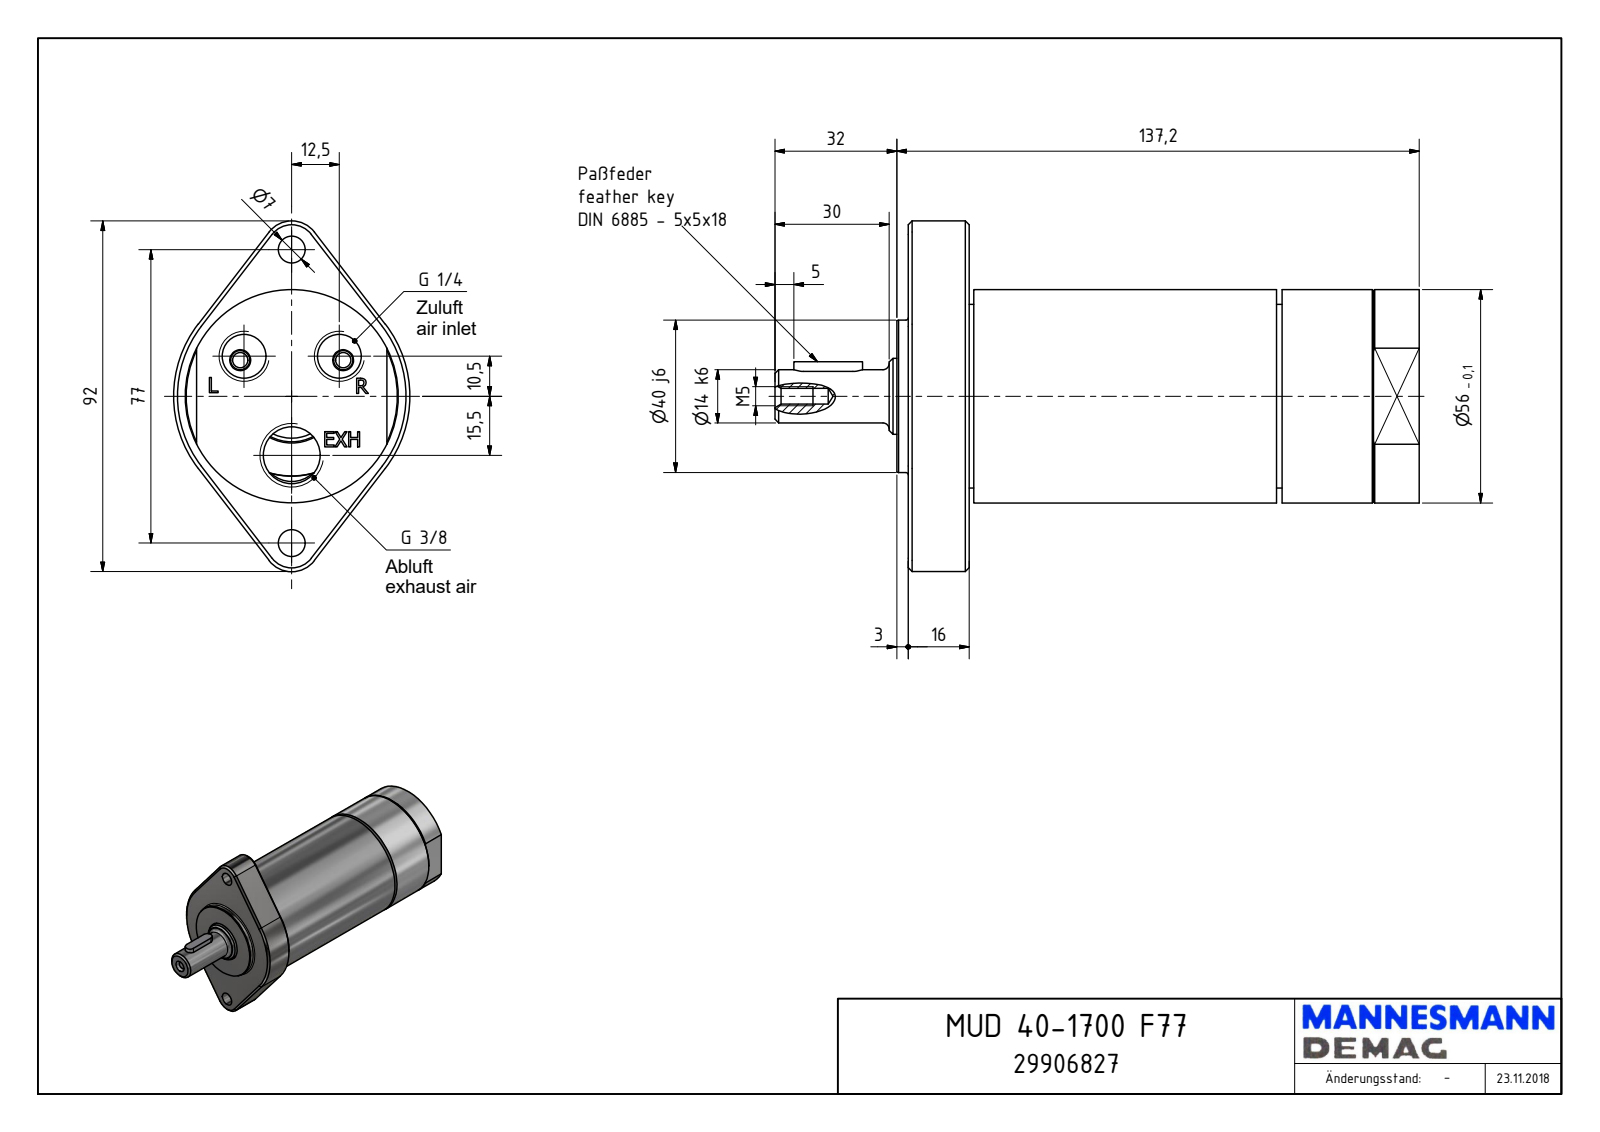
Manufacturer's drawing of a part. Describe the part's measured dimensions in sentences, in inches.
The part is named "MUD 40-1700 F77_29906827". Its 3-D file was written by "Autodesk Inventor 2018 (AUTOMOTIVE_DESIGN)". It is 1 solid with 189 faces: 104 planar, 35 cylindrical and 50 other. Overall it measures 6.661 by 3.622 by 2.441 inches. Its volume is 21.41 cubic inches and its surface area 62.99 square inches. Round holes: 2 of diameter 0.276, 2 of diameter 0.451, 1 of diameter 0.163, 1 of diameter 0.589, 1 of diameter 0.827, 1 of diameter 0.837, 1 of diameter 0.927, 1 of diameter 1.024, 1 of diameter 1.905. Round bosses or shafts: 1 of diameter 2.205, 1 of diameter 1.897, 1 of diameter 1.575, 1 of diameter 0.785, 1 of diameter 0.551. Partial cylindrical surfaces (rounded edges, fillets, slot ends): 2 of radius 0.098, 2 of radius 0.236, 2 of radius 0.295, 1 of radius 0.851, 1 of radius 0.906, 1 of radius 1.22. The main face-to-face distances are 5.283, 0.63, 4.654, 0.118, 0.748, 5.402, 0.795, 0.677, 0.047, 4.606. The hole center spacings are 0.643, 1.136, 1.207, 1.516, 1.991, 0.61, 0.906, 0.984.
